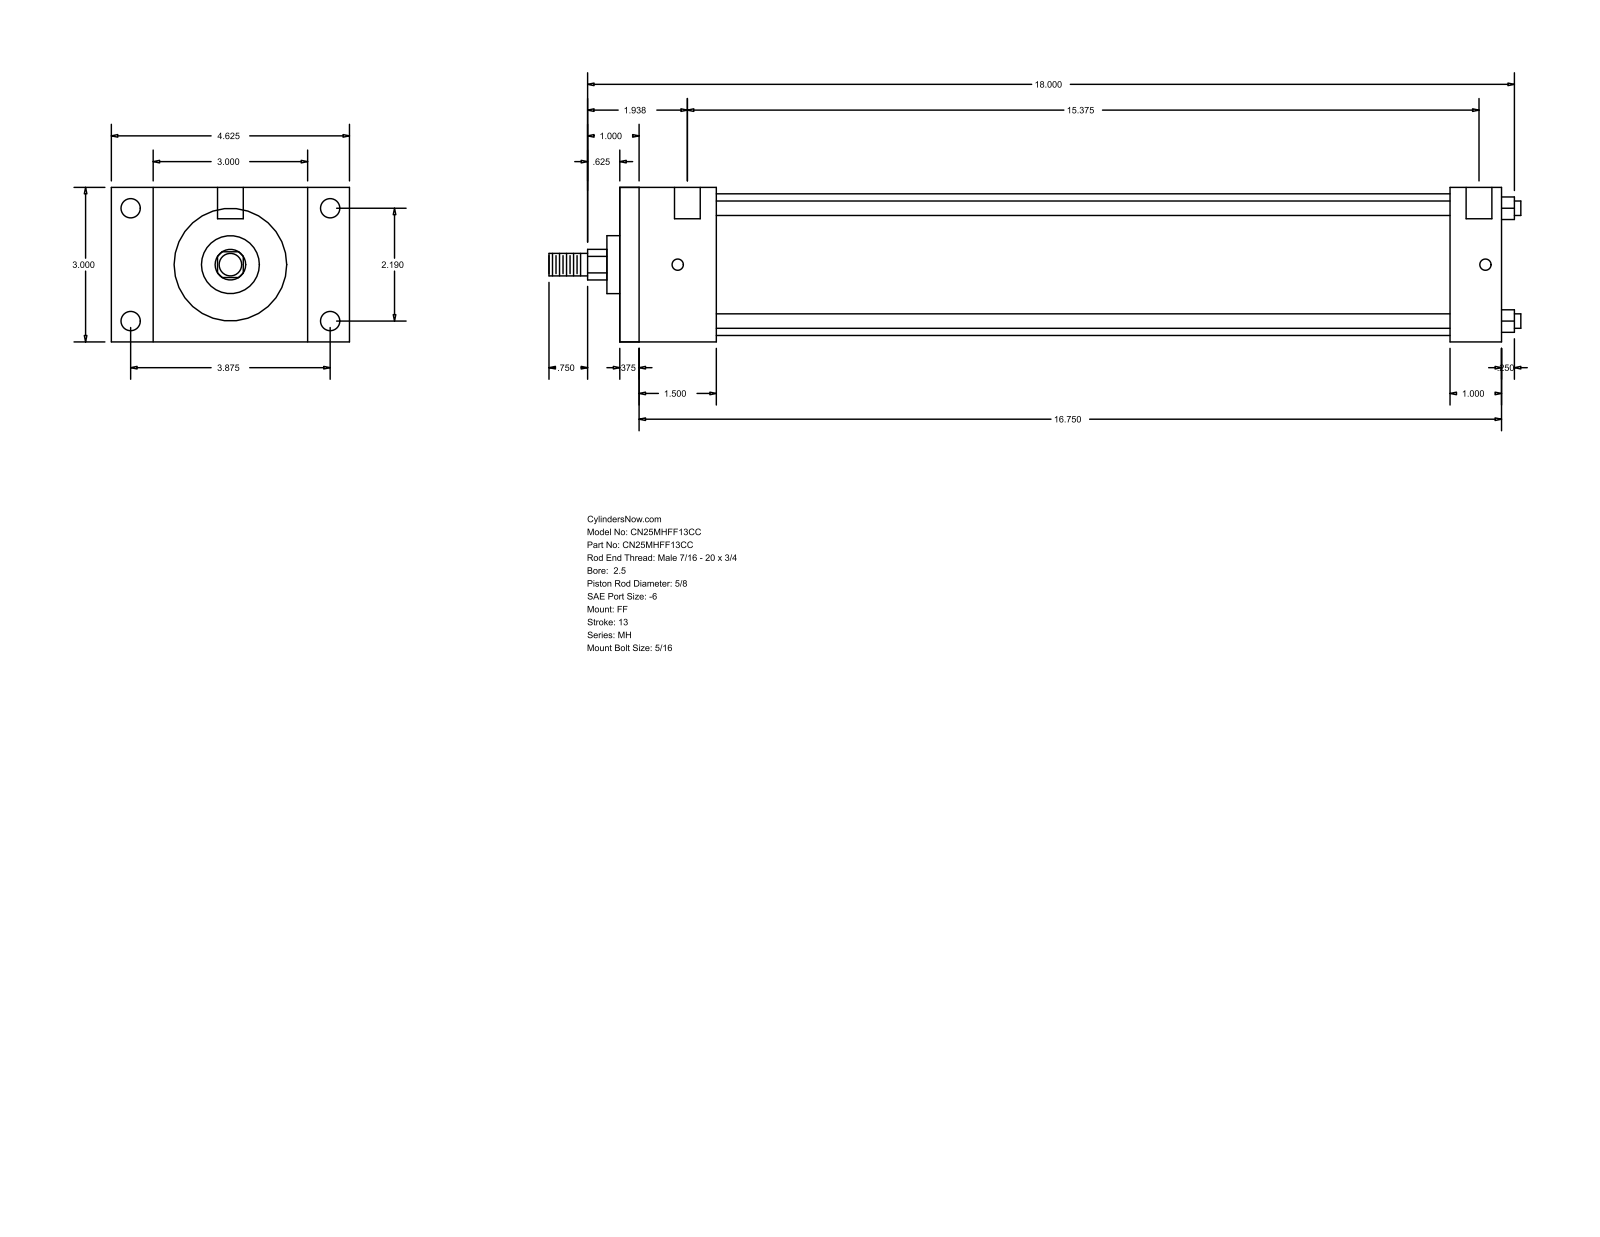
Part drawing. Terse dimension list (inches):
name: MH_FF__0250_0.625
written by: GSSL Pune (CONFIG_CONTROL_DESIGN)
unit: in
bodies: 0 solids, 92 faces (64 planar, 28 cylindrical, 0 other)
size: 18.875 × 4.625 × 3
holes: 4× ⌀0.219, 4× ⌀0.375, 2× ⌀0.5
bosses: 4× ⌀0.281, 1× ⌀2.75, 1× ⌀1.125, 1× ⌀0.625, 1× ⌀0.437
rounds: 1× R0.297
face distances: 3, 17.125, 16.75, 0.375, 1, 1.875, 16.125, 1.5, 15.75, 14.25
hole spacings: 2.19, 3.875, 4.451, 15.687, 0.125, 0.187, 15.375, 15.5
